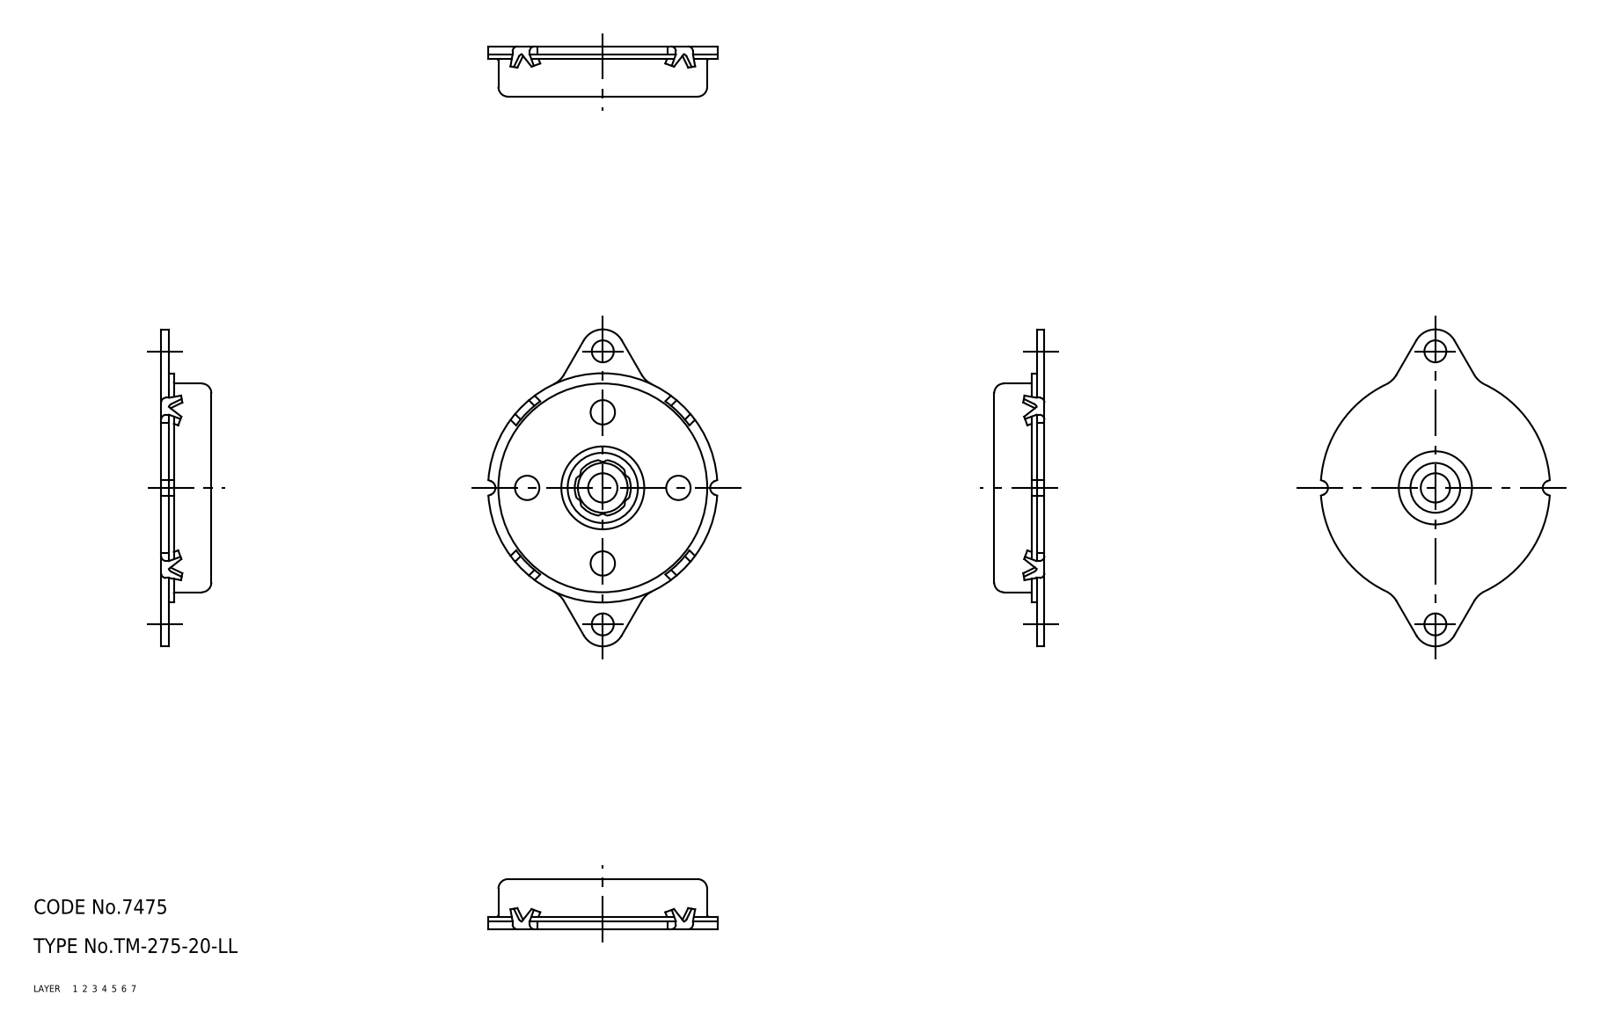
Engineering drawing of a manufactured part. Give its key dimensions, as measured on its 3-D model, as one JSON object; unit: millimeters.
{"part_name": "inner ring; TM_275_20_LL_1080_36", "step_written_by": "CADfix (AUTOMOTIVE_DESIGN)", "units": "millimeters", "bodies": {"solids": 2, "faces": 169, "planar": 0, "cylindrical": 0, "other": 169}, "overall_size": [65, 46.89, 10.3], "volume_mm3": 15252, "surface_area_mm2": 6866}
